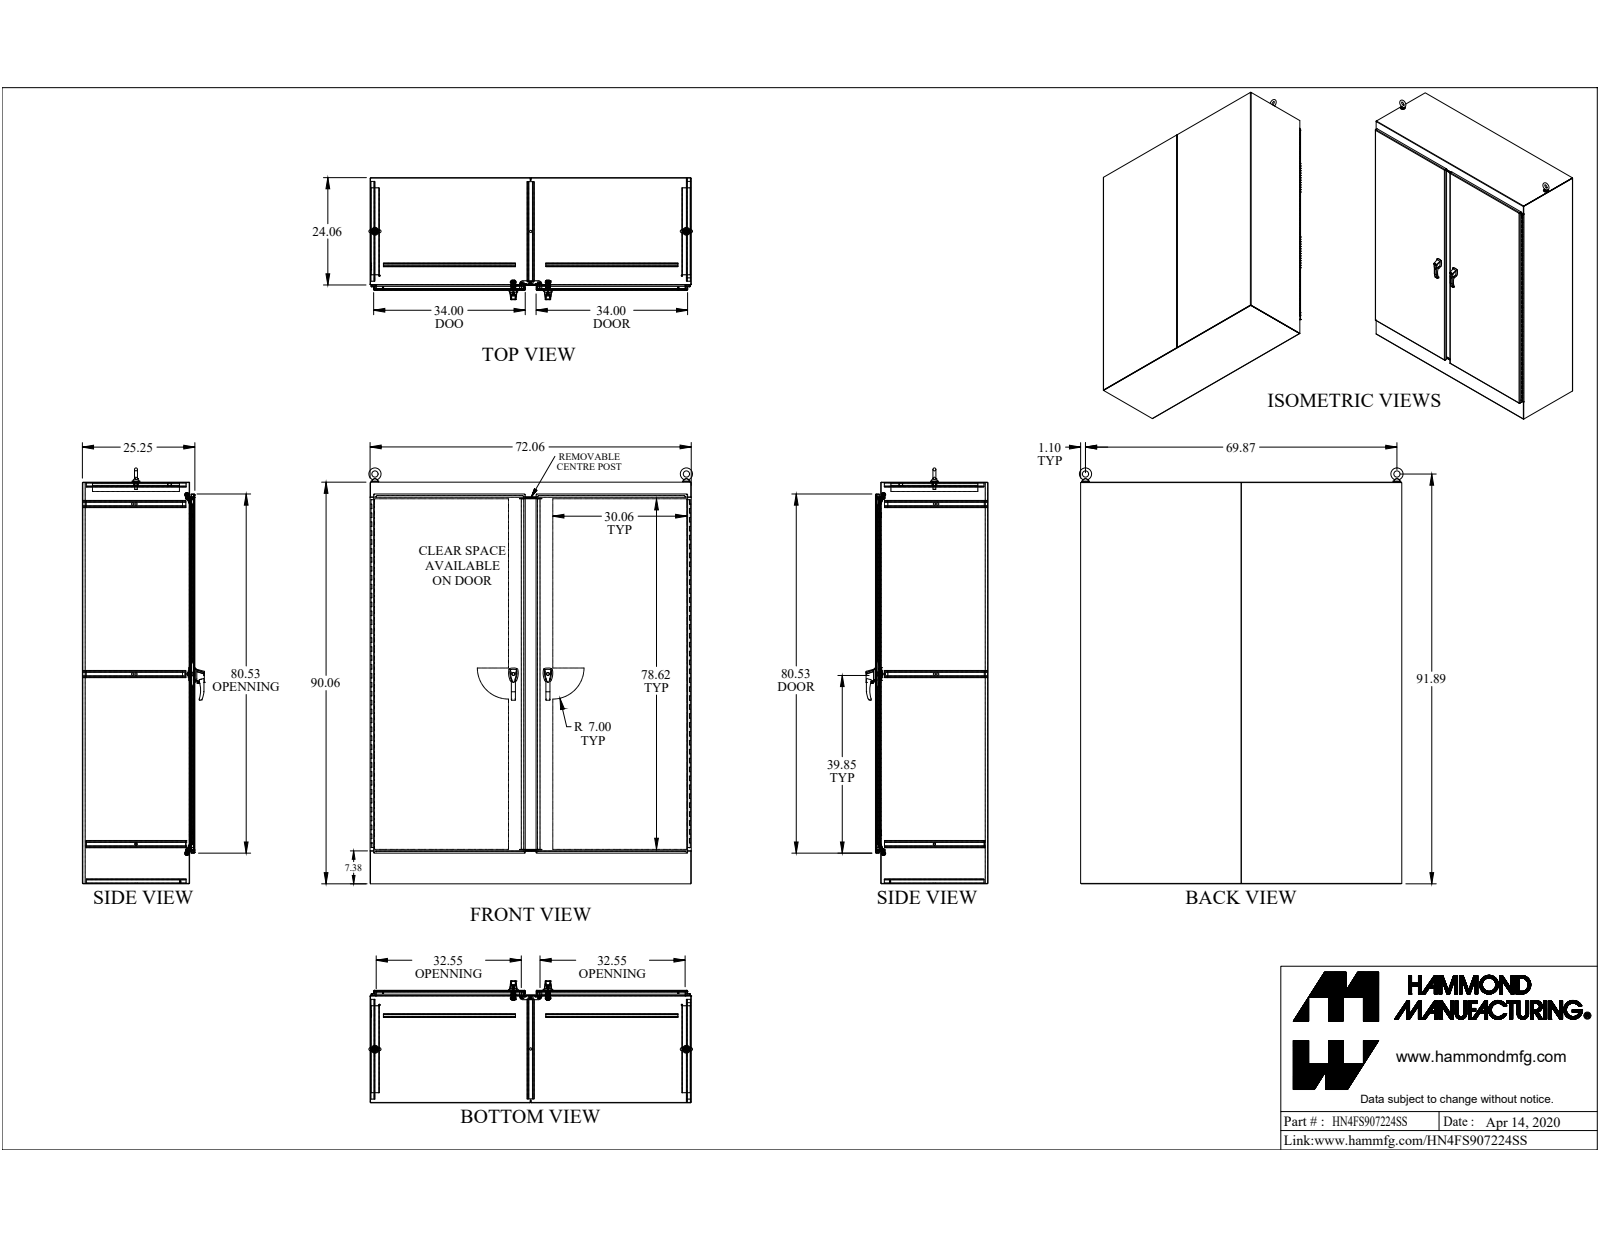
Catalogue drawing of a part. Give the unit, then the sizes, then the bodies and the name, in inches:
Units: inches
Overall size (bounding box): 93.256 × 72.604 × 27.362
Round holes (diameter × count): ⌀0.304 ×26, ⌀0.35 ×8, ⌀0.25 ×7, ⌀0.5 ×7, ⌀0.257 ×4, ⌀0.28 ×4, ⌀0.281 ×4, ⌀0.313 ×4, ⌀0.39 ×4, ⌀0.413 ×4, ⌀0.201 ×3, ⌀0.313 ×3
Round bosses / shafts (diameter × count): ⌀1 ×4, ⌀0.75 ×4, ⌀0.63 ×4, ⌀0.625 ×4, ⌀0.44 ×4, ⌀0.37 ×4, ⌀0.313 ×4, ⌀0.25 ×4
Partial cylindrical surfaces — rounded edges, fillets, slot ends (radius × count): R0.043 ×54, R0.138 ×48, R0.5 ×33, R0.018 ×32, R0.1 ×28, R0.125 ×27, R0.06 ×24, R0.036 ×16
Main face-to-face distances: 0.095, 25.152, 25.057, 25.247, 71.965, 89.965, 71.87, 1.187, 23.965, 72.06
Hole centre spacings: 6, 70.584, 12, 71.345, 18, 72.595, 24, 74.311
Volume: 2 329 in³ · Surface area: 49 232 in²
Bodies: 106 solids, 3187 faces (1671 planar, 1270 cylindrical, 246 other)
Part name (STEP PRODUCT): HN4FS907224SS
STEP written by: SolidWorks 2019 (CONFIG_CONTROL_DESIGN)
